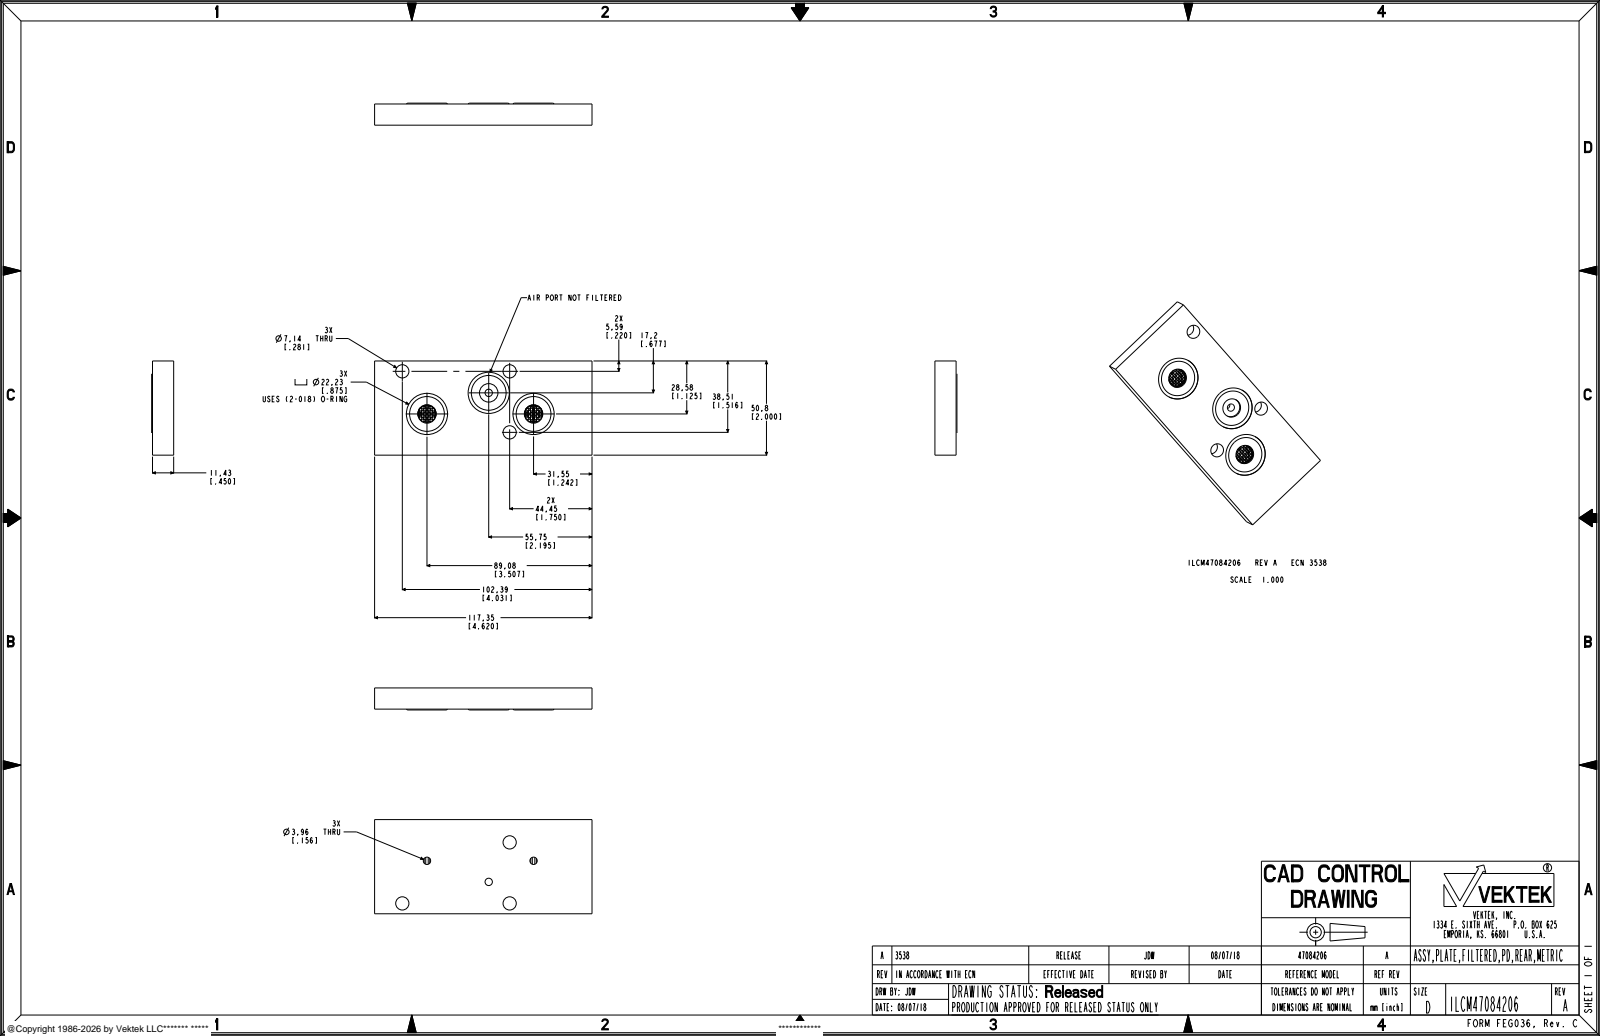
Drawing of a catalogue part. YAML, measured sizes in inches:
part_name: "ILCM47084206"
step_written_by: "PRO/ENGINEER BY PARAMETRIC TECHNOLOGY CORPORATION, 2013320 (AUTOMOTIVE_DESIGN)"
units: inches
bodies: {solids: 1, faces: 486, planar: 168, cylindrical: 308, other: 10}
overall_size: [4.62, 2, 0.468]
volume: 3.926
surface_area: 29.87
round_holes:
  - {diameter: 0.062, count: 32}
  - {diameter: 0.156, count: 3}
  - {diameter: 0.281, count: 3}
  - {diameter: 0.392, count: 3}
  - {diameter: 0.875, count: 3}
  - {diameter: 0.265, count: 2}
  - {diameter: 0.29, count: 2}
  - {diameter: 0.411, count: 2}
round_bosses_or_shafts:
  - {diameter: 0.375, count: 2}
  - {diameter: 0.371, count: 2}
partial_cylinders:
  - {radius: 0.031, count: 32}
  - {radius: 0.021, count: 14}
  - {radius: 0.016, count: 8}
  - {radius: 0.026, count: 6}
  - {radius: 0.01, count: 4}
  - {radius: 0.015, count: 4}
  - {radius: 0.023, count: 4}
  - {radius: 0.15, count: 2}
face_to_face_distances: [0.45, 2, 0.398, 0.052, 4.62, 0.049, 0.098, 0.129, 0.031, 2.265]
hole_center_spacings: [0.067, 0.148, 0.133, 0.21, 0.24, 0.094, 0.149, 2.265]
